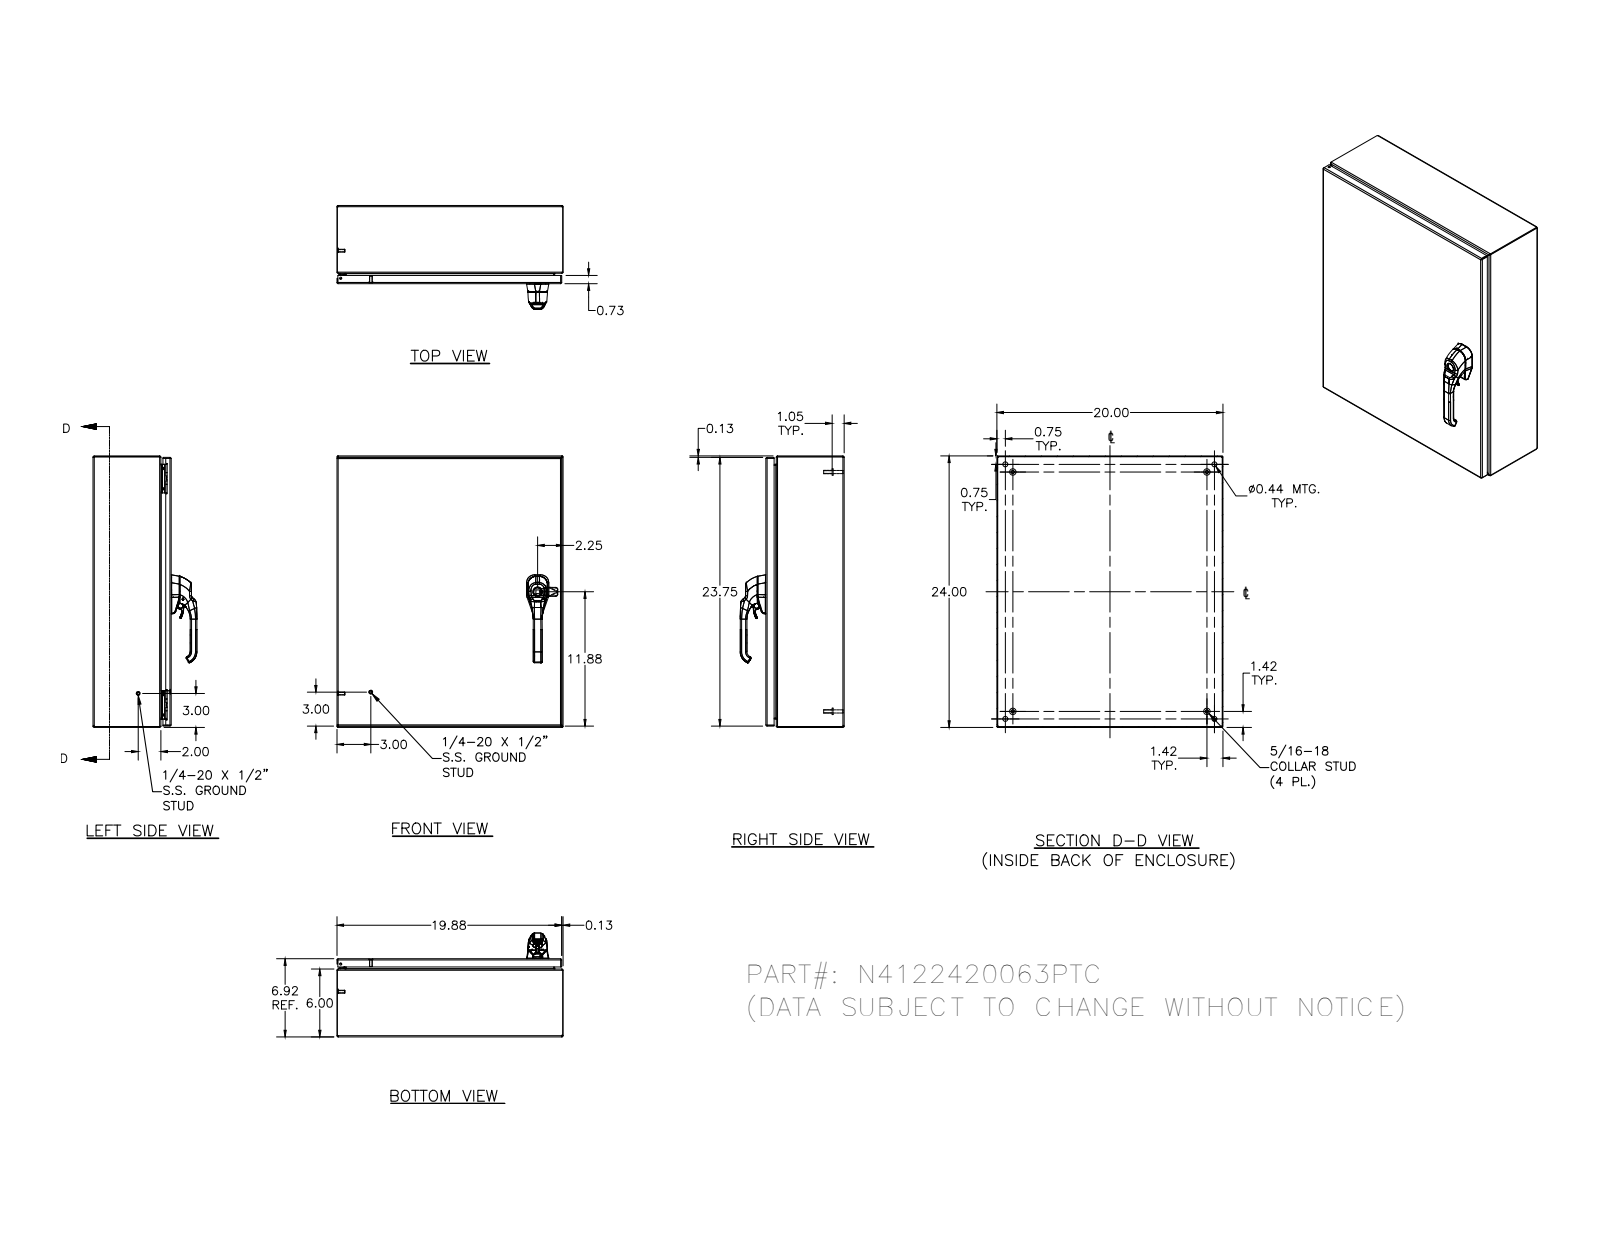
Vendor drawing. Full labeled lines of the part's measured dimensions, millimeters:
Part name (STEP PRODUCT): N4122420063PTC
STEP written by: SolidWorks 2018 (AUTOMOTIVE_DESIGN)
Units: millimetres
Bodies: 29 solids, 1333 faces (433 planar, 495 cylindrical, 405 other)
Overall size (bounding box): 609.6 × 508 × 231
Volume: 2 178 000 mm³ · Surface area: 2 185 000 mm²
Round holes (diameter × count): ⌀4.8 ×5, ⌀2.4 ×4, ⌀3.9 ×4, ⌀4.2 ×4, ⌀4.4 ×4, ⌀11.1 ×4, ⌀4 ×2, ⌀4.7 ×1, ⌀10.5 ×1
Round bosses / shafts (diameter × count): ⌀6.4 ×10, ⌀14.3 ×4, ⌀9.1 ×4, ⌀8.1 ×4, ⌀7.6 ×4, ⌀7 ×4, ⌀6.5 ×4, ⌀4.2 ×4
Partial cylindrical surfaces — rounded edges, fillets, slot ends (radius × count): R0.8 ×30, R1.3 ×26, R2.7 ×20, R0.4 ×18, R3.2 ×14, R0.5 ×11, R0.8 ×8, R1.7 ×8
Main face-to-face distances: 1.9, 173.8, 175.7, 171.9, 506.1, 607.7, 508, 504.2, 609.6, 605.8
Hole centre spacings: 507.9, 479.3, 0.4, 16.8, 524.7, 0.5, 12.7, 16.5
